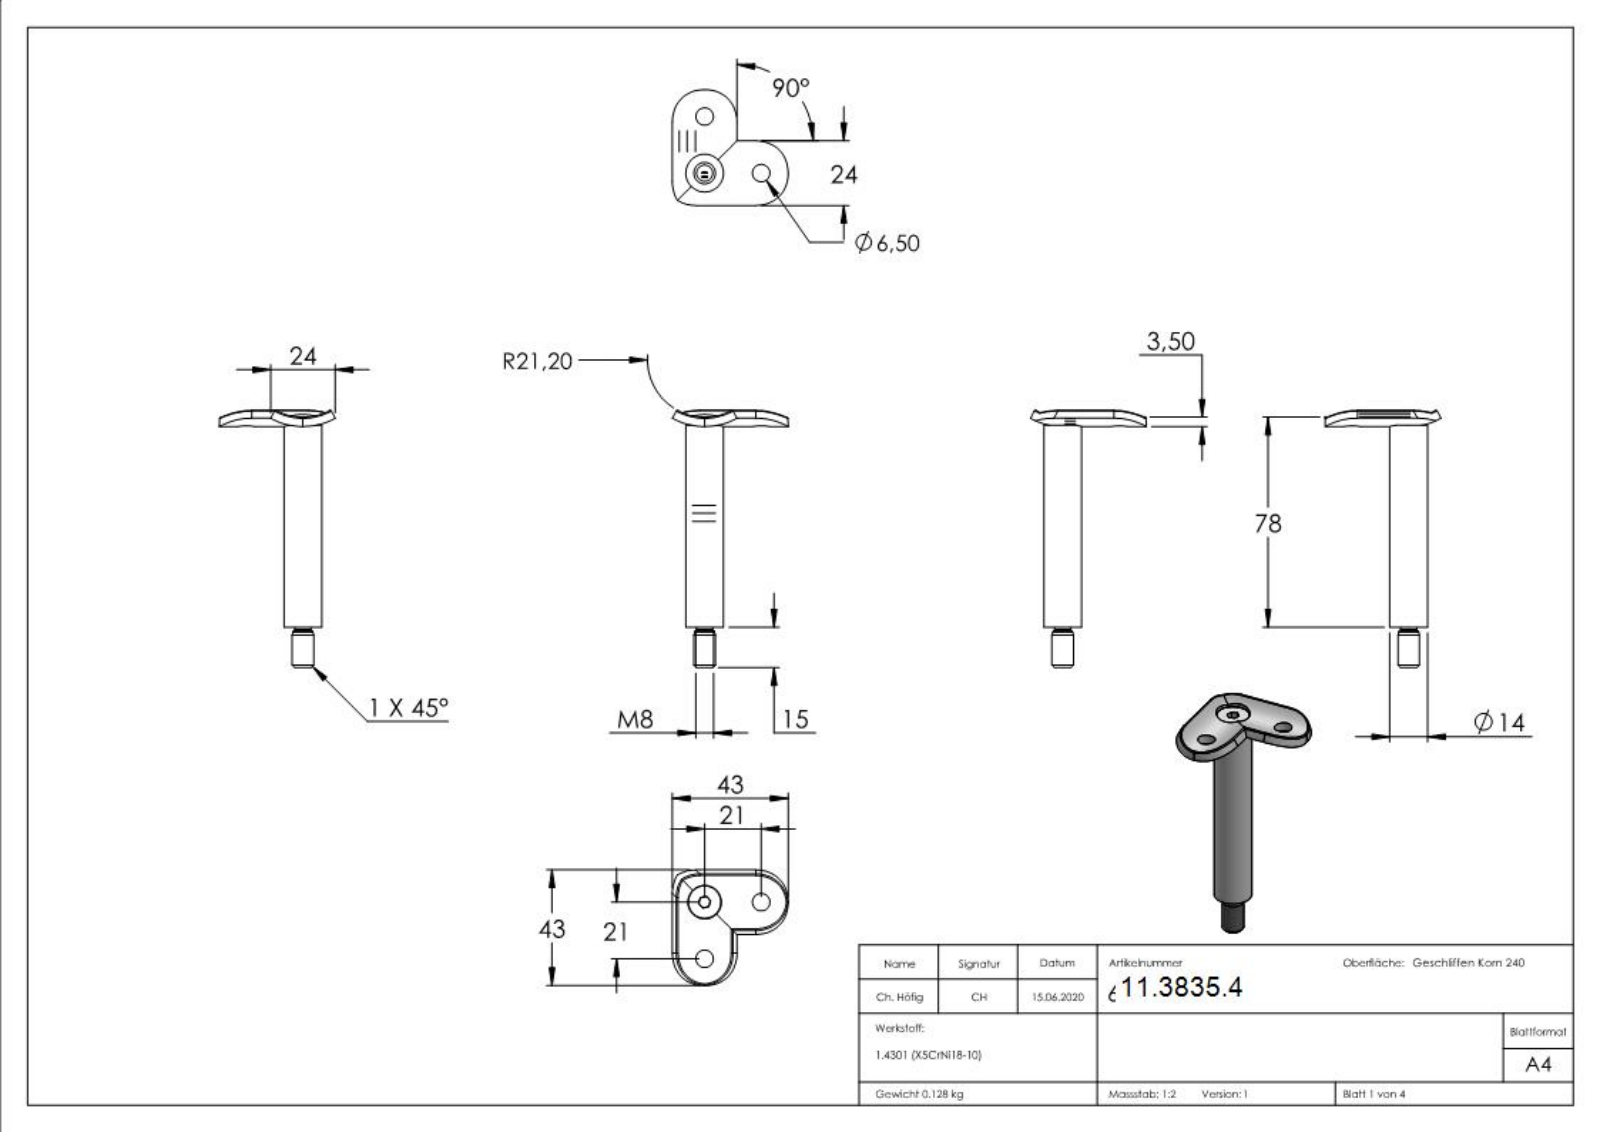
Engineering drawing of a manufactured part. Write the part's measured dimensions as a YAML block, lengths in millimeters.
part_name: "60174-240; 60179-240_60179-240; 50236-Konfig_50233-240; DIN-7991_-_DIN7991 M6x16_DIN7991 M6x16"
step_written_by: "SolidWorks 2015 (CONFIG_CONTROL_DESIGN)"
units: millimeters
bodies: {solids: 3, faces: 297, planar: 138, cylindrical: 35, other: 124}
overall_size: [95.5, 43, 43]
volume: 16220
surface_area: 7922
round_holes:
  - {diameter: 6.5, count: 2}
  - {diameter: 5, count: 1}
  - {diameter: 8.5, count: 1}
  - {diameter: 12.5, count: 1}
  - {diameter: 14, count: 1}
round_bosses_or_shafts:
  - {diameter: 12, count: 1}
  - {diameter: 8, count: 1}
  - {diameter: 6, count: 1}
partial_cylinders:
  - {radius: 0.5, count: 4}
  - {radius: 12, count: 4}
  - {radius: 21.2, count: 2}
  - {radius: 24.7, count: 2}
  - {radius: 10, count: 1}
face_to_face_distances: [2.55, 90, 92.55, 4, 76.55, 13.45, 16, 0.45, 89.55, 13]
hole_center_spacings: [21, 29.7]
